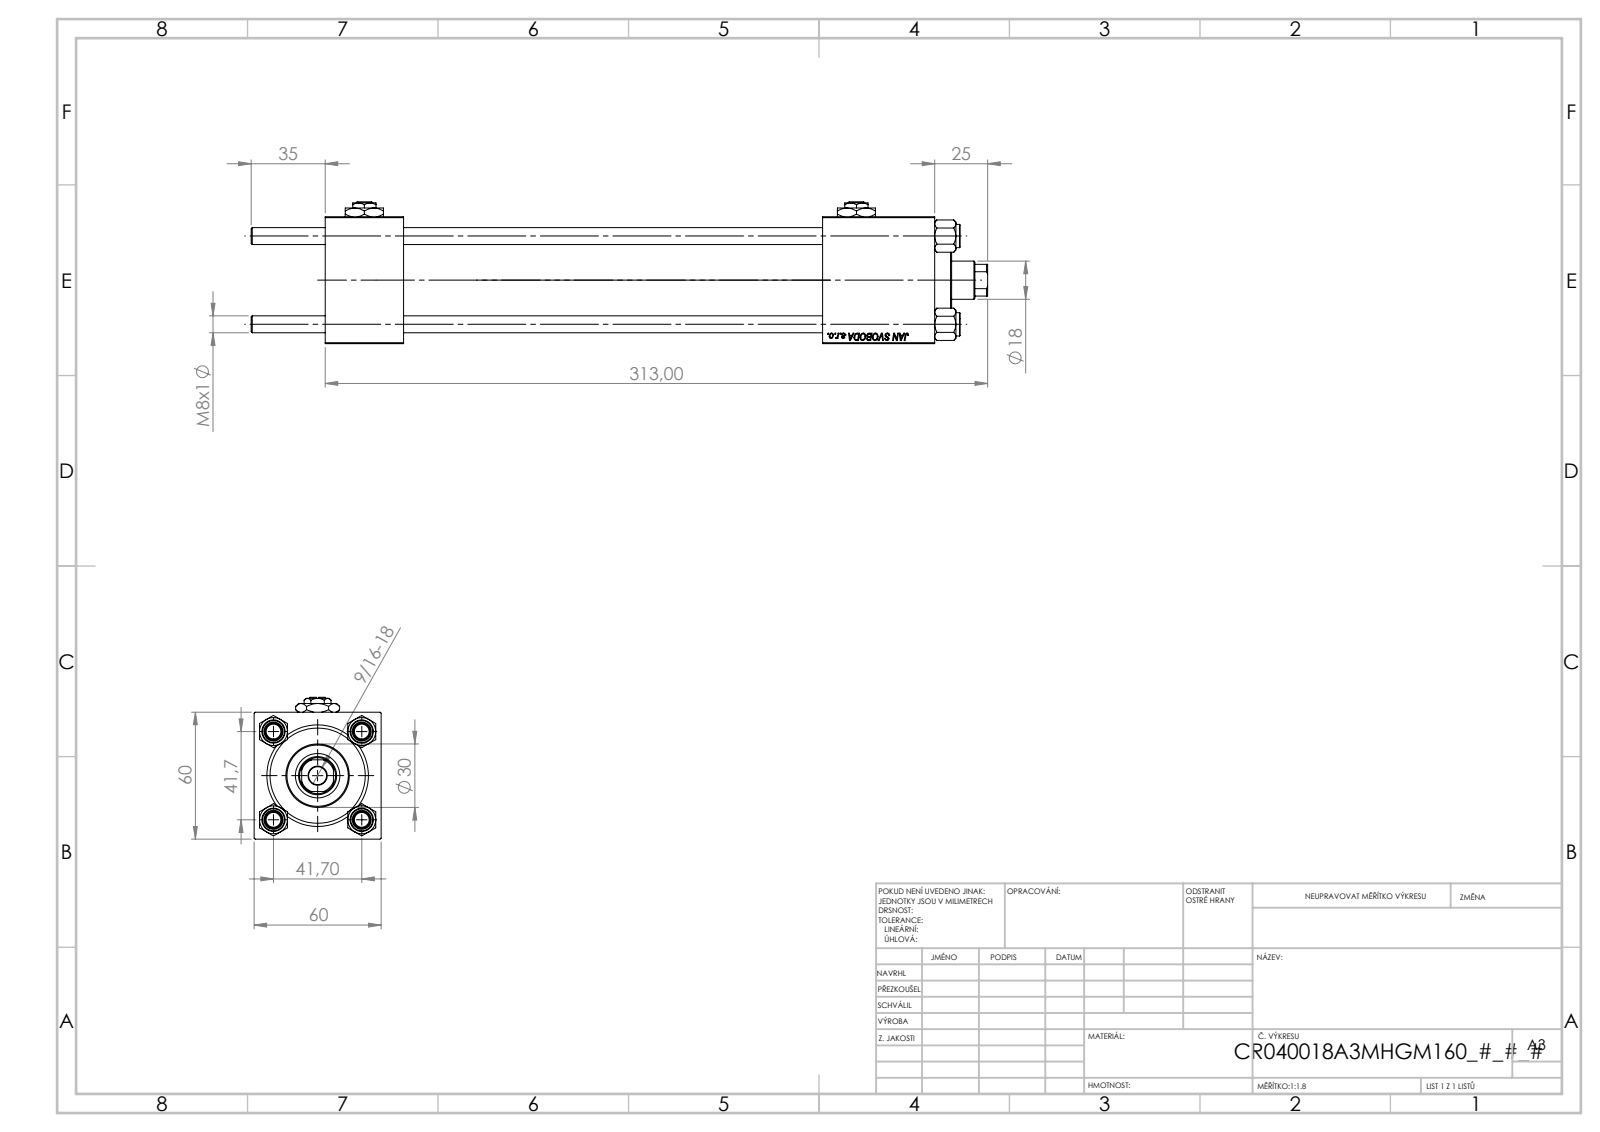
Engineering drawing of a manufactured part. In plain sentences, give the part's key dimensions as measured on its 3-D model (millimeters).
The part is named "NUT_M5; V215CR_VCP; Zatka_pro_OIL_PORT; V215_VC_A (+2 more)". Its 3-D file was written by "SolidWorks 2019 (CONFIG_CONTROL_DESIGN)". It is 13 solids with 1235 faces: 569 planar, 88 cylindrical and 578 other. Overall it measures 348 by 67 by 60 millimeters. Its volume is 531 165 cubic millimeters and its surface area 176 741 square millimeters. Round holes: 4 of diameter 8, 2 of diameter 7, 2 of diameter 16.66, 2 of diameter 24, 1 of diameter 8.5, 1 of diameter 18, 1 of diameter 21, 1 of diameter 31, 1 of diameter 40, 1 of diameter 45. Round bosses or shafts: 4 of diameter 11, 1 of diameter 46, 1 of diameter 30. Partial cylindrical surfaces (rounded edges, fillets, slot ends): 1 of radius 8.5. The main face-to-face distances are 60, 37, 288, 251, 53, 235, 198, 259.3, 222.3, 24.3. The hole center spacings are 29.49, 41.7, 58.97, 232.5.
